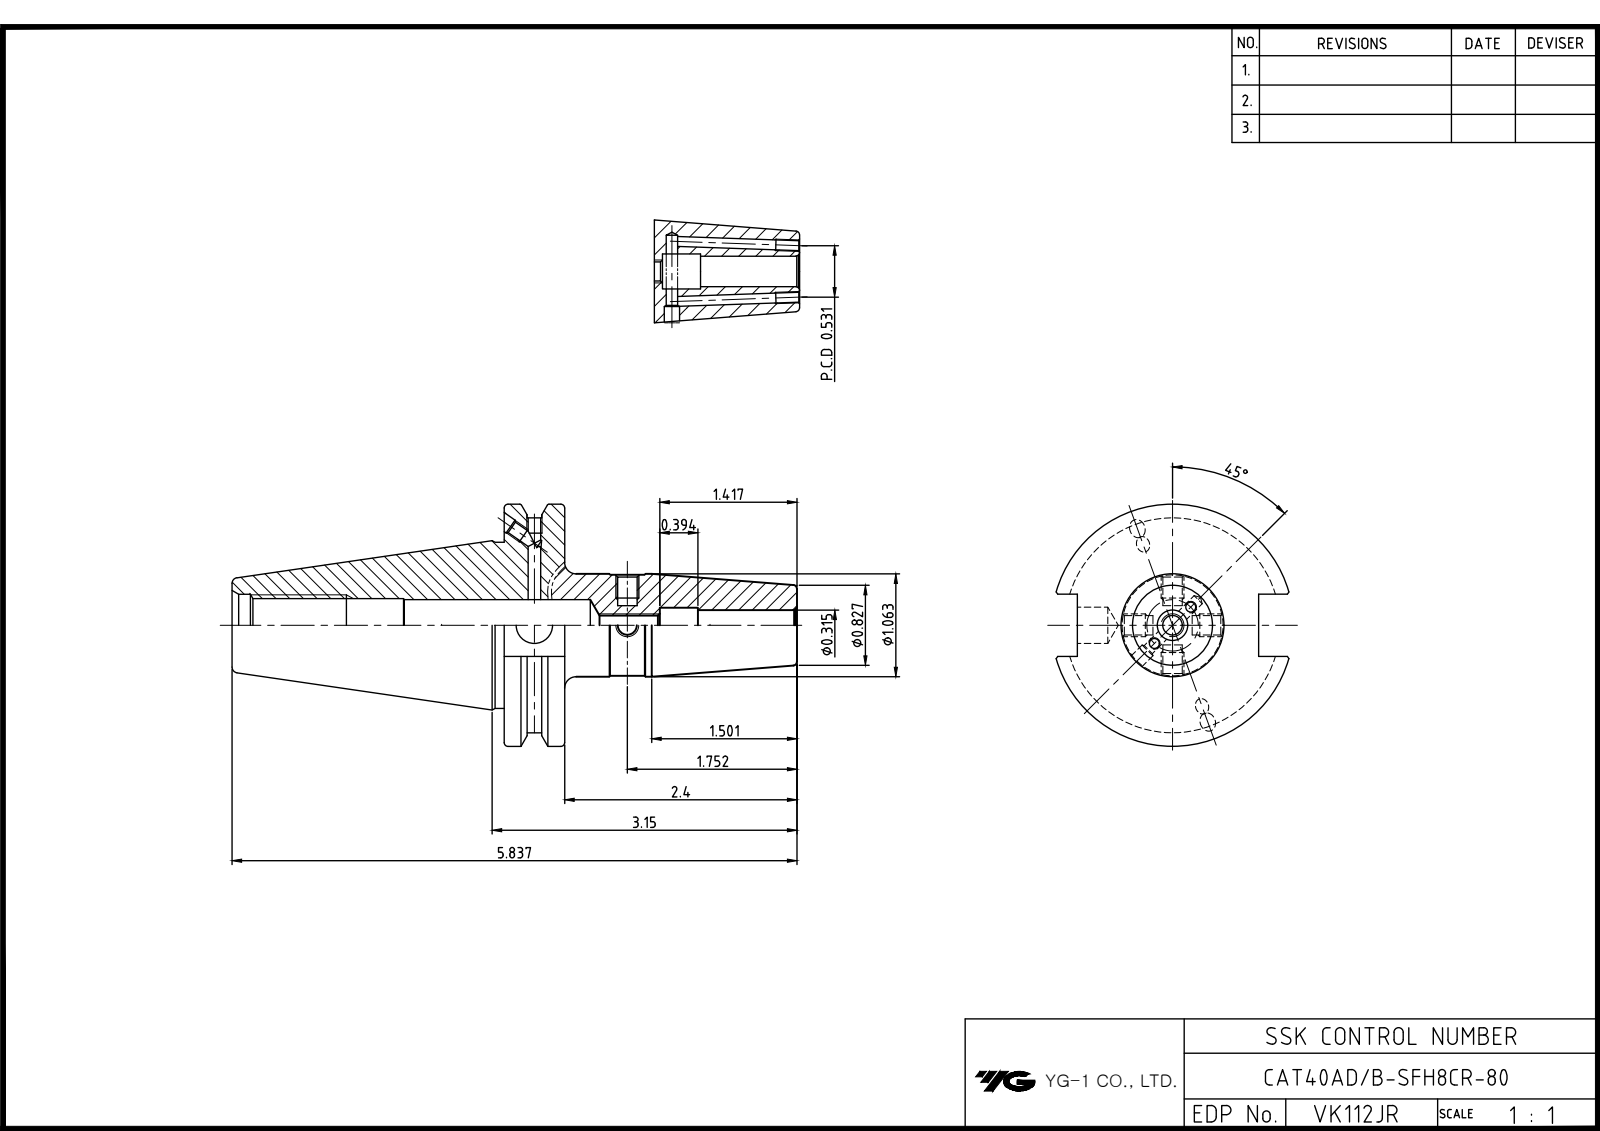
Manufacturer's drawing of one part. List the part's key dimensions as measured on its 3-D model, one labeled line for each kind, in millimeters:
Part name (STEP PRODUCT): LO-CAT40ADB-SFH8CR-80
STEP written by: Autodesk Inventor 2025 (AUTOMOTIVE_DESIGN)
Units: millimetres
Bodies: 1 solid, 90 faces (37 planar, 30 cylindrical, 23 other)
Overall size (bounding box): 148.25 × 63.5 × 61.09
Volume: 128 503 mm³ · Surface area: 27 143 mm²
Round holes (diameter × count): ⌀3.24 ×4, ⌀2.46 ×2, ⌀4 ×2, ⌀4.2 ×2, ⌀4.92 ×1, ⌀8 ×1, ⌀9.2 ×1, ⌀9.53 ×1, ⌀13.39 ×1, ⌀16.3 ×1
Round bosses / shafts (diameter × count): ⌀63.5 ×1, ⌀43.6 ×1, ⌀27 ×1
Partial cylindrical surfaces — rounded edges, fillets, slot ends (radius × count): R28.15 ×1
Main face-to-face distances: 15.88, 76.83, 60.95, 47.6, 16.38, 71.42, 87.3, 148.25, 77.47, 6.05
